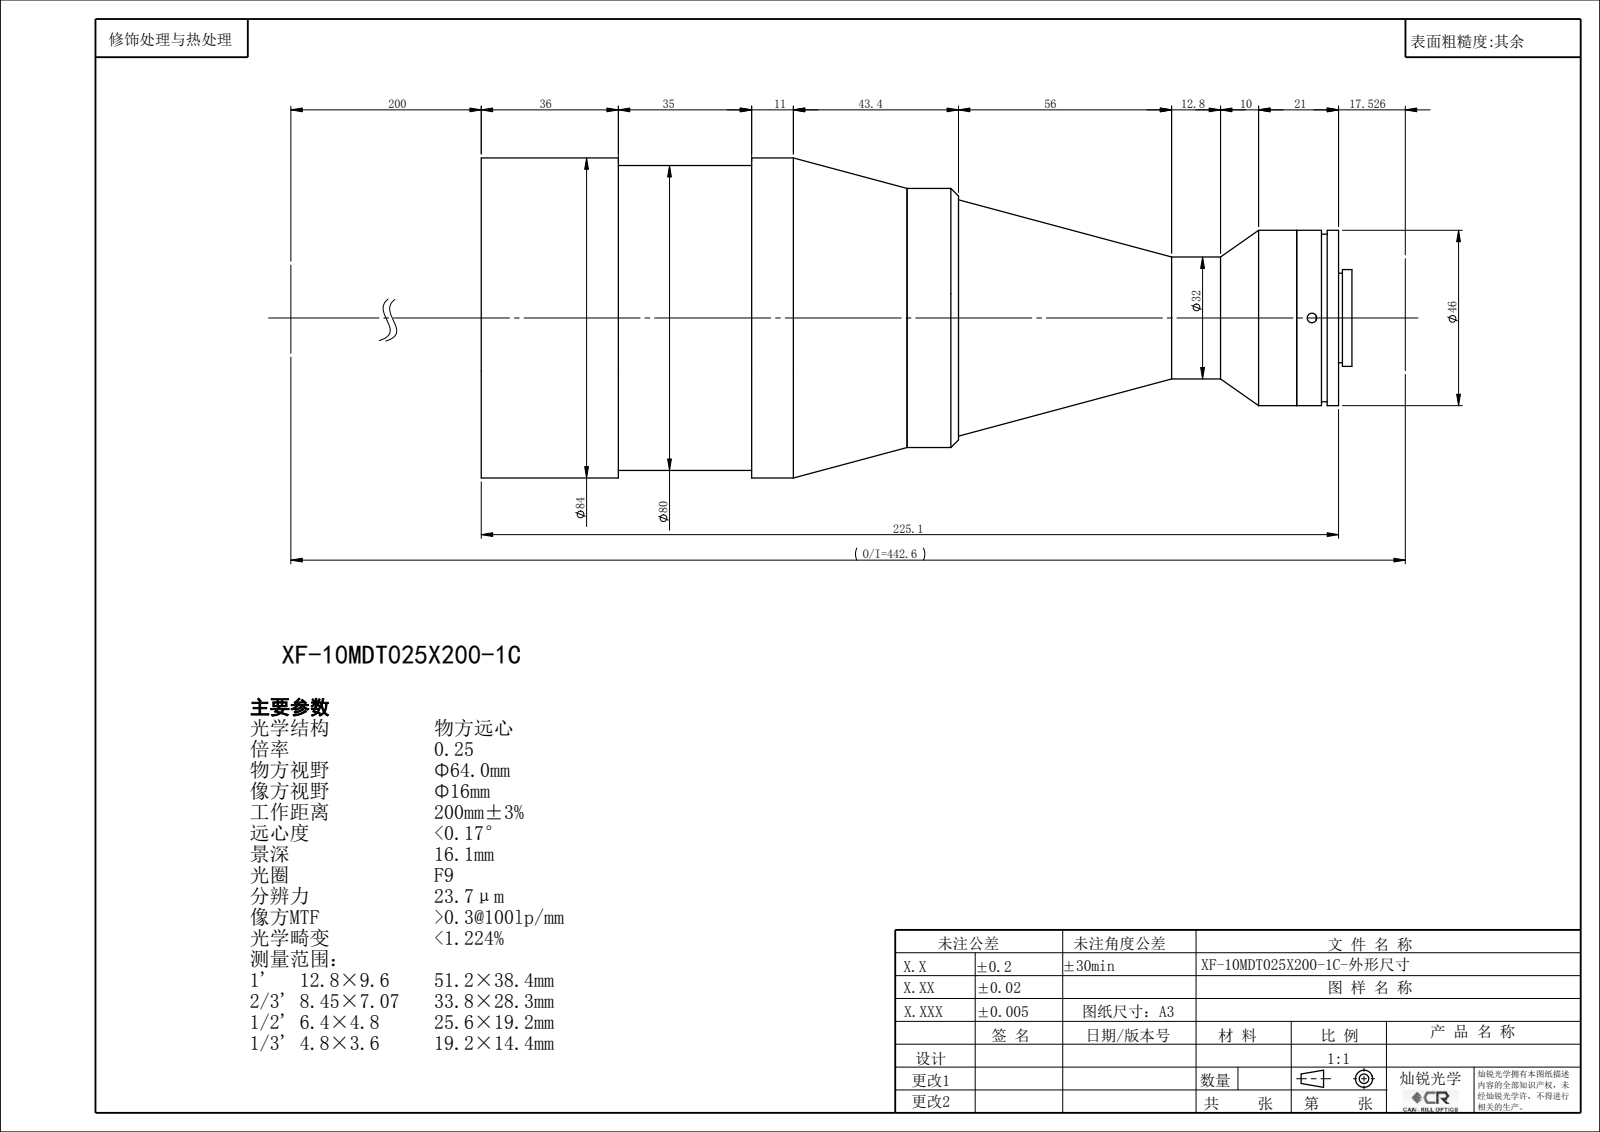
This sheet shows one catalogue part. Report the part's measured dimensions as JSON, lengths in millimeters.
{"part_name": "XF-5MDT025X200-1C", "step_written_by": "SolidWorks 2014 (CONFIG_CONTROL_DESIGN)", "units": "millimeters", "bodies": {"solids": 0, "faces": 90, "planar": 32, "cylindrical": 44, "other": 14}, "overall_size": [228.63, 84, 84], "round_holes": [[2.5, 3], [20.5, 1], [27.4, 1], [30, 1], [62, 1], [71, 1], [77, 1], [79, 1]], "round_bosses_or_shafts": [[84, 1], [80, 1], [68, 1], [46, 1], [44, 1], [32, 1], [25.4, 1], [23.5, 1]], "face_to_face_distances": [113.32, 102.32, 11, 111.81, 214.13, 225.13, 36, 75.81, 178.13, 189.13]}
